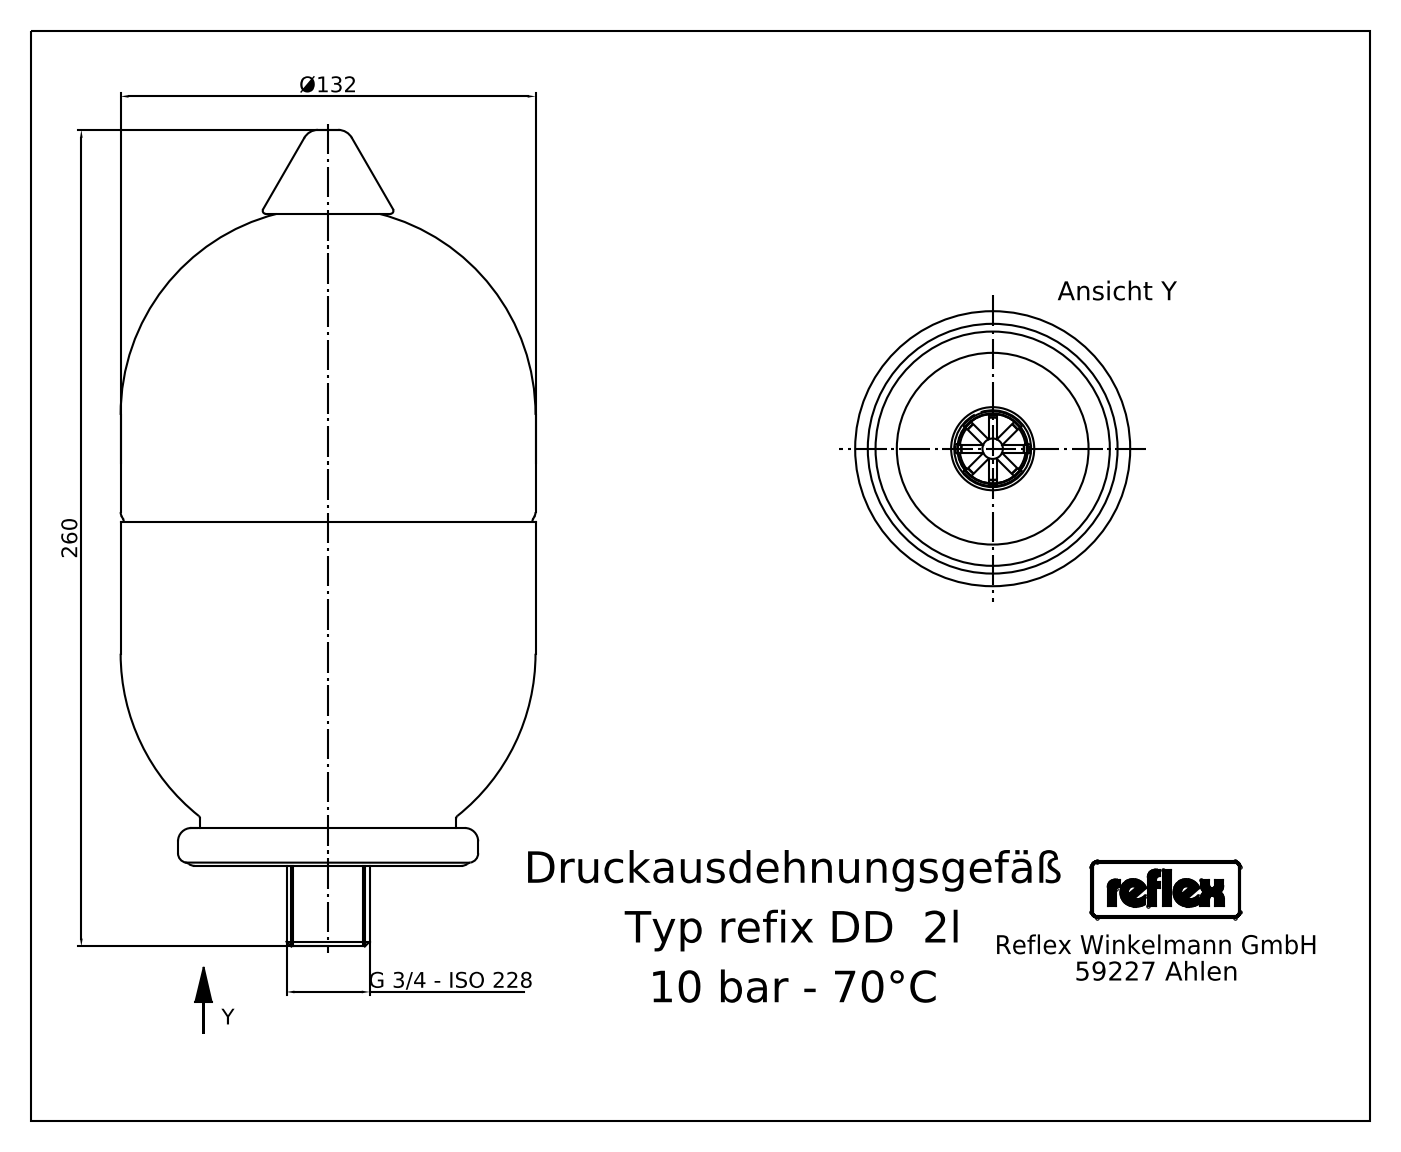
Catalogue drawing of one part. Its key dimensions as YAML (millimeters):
step_written_by: "Mechanical Desktop 2008 (CONFIG_CONTROL_DESIGN)"
units: millimeters
bodies: {solids: 13, faces: 150, planar: 72, cylindrical: 44, other: 34}
overall_size: [260, 132.32, 132]
volume: 2480000
surface_area: 179097
round_holes:
  - {diameter: 14.1, count: 1}
  - {diameter: 18.9, count: 1}
round_bosses_or_shafts:
  - {diameter: 132, count: 1}
  - {diameter: 96, count: 1}
  - {diameter: 82, count: 1}
  - {diameter: 26.9, count: 1}
  - {diameter: 17.1, count: 1}
  - {diameter: 9, count: 1}
  - {diameter: 6, count: 1}
partial_cylinders:
  - {radius: 1.12, count: 4}
  - {radius: 0.45, count: 3}
  - {radius: 0.77, count: 2}
  - {radius: 1.35, count: 2}
  - {radius: 1.85, count: 2}
  - {radius: 1.88, count: 2}
  - {radius: 2.54, count: 2}
  - {radius: 0.56, count: 1}
face_to_face_distances: [0.5, 86.5, 86, 87, 36.5, 37, 123, 123.5, 18, 54.5]
